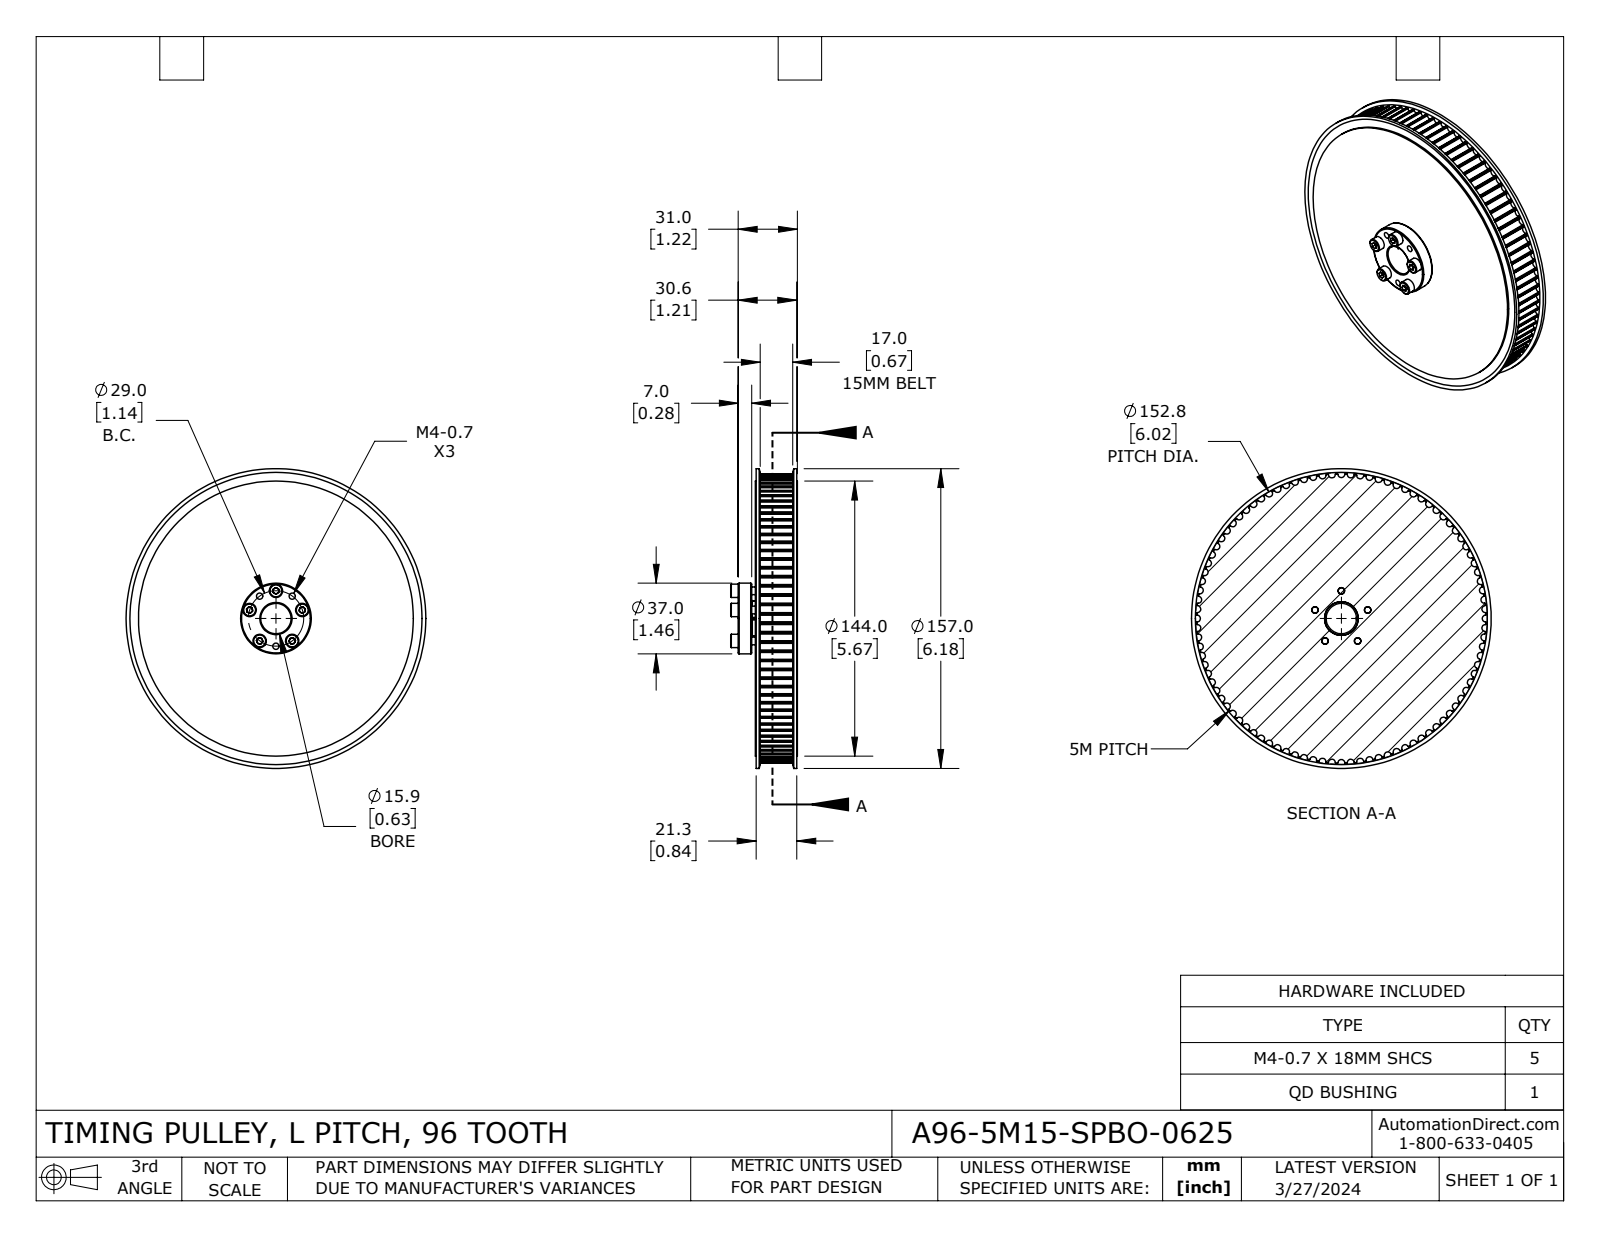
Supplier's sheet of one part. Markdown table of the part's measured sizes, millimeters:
| quantity | value |
| --- | --- |
| part name | A96-5M15-SPBO-0625 |
| STEP written by | SolidWorks 2021 (CONFIG_CONTROL_DESIGN) |
| units | millimeters |
| bodies | 9 solids, 714 faces (101 planar, 547 cylindrical, 66 other) |
| overall size | 157 × 157 × 35 |
| volume | 390 846 mm³ |
| surface area | 72 823 mm² |
| round holes (diameter × count) | 3.3 × 8, 4.5 × 5, 15.88 × 1, 18.47 × 1, 144 × 1 |
| round bosses / shafts (diameter × count) | 7 × 5, 4 × 5, 157 × 1, 37 × 1 |
| partial cylindrical surfaces (radius × count) | 0.3 × 192, 1.82 × 96, 75.83 × 1 |
| main face-to-face distances | 22, 2.5, 19.5, 0.9, 21.1, 1.6, 18.6, 17, 20.2, 9 |
| hole center spacings | 14.5, 27.58, 8.96, 23.46, 17.05, 29, 17.04 |
